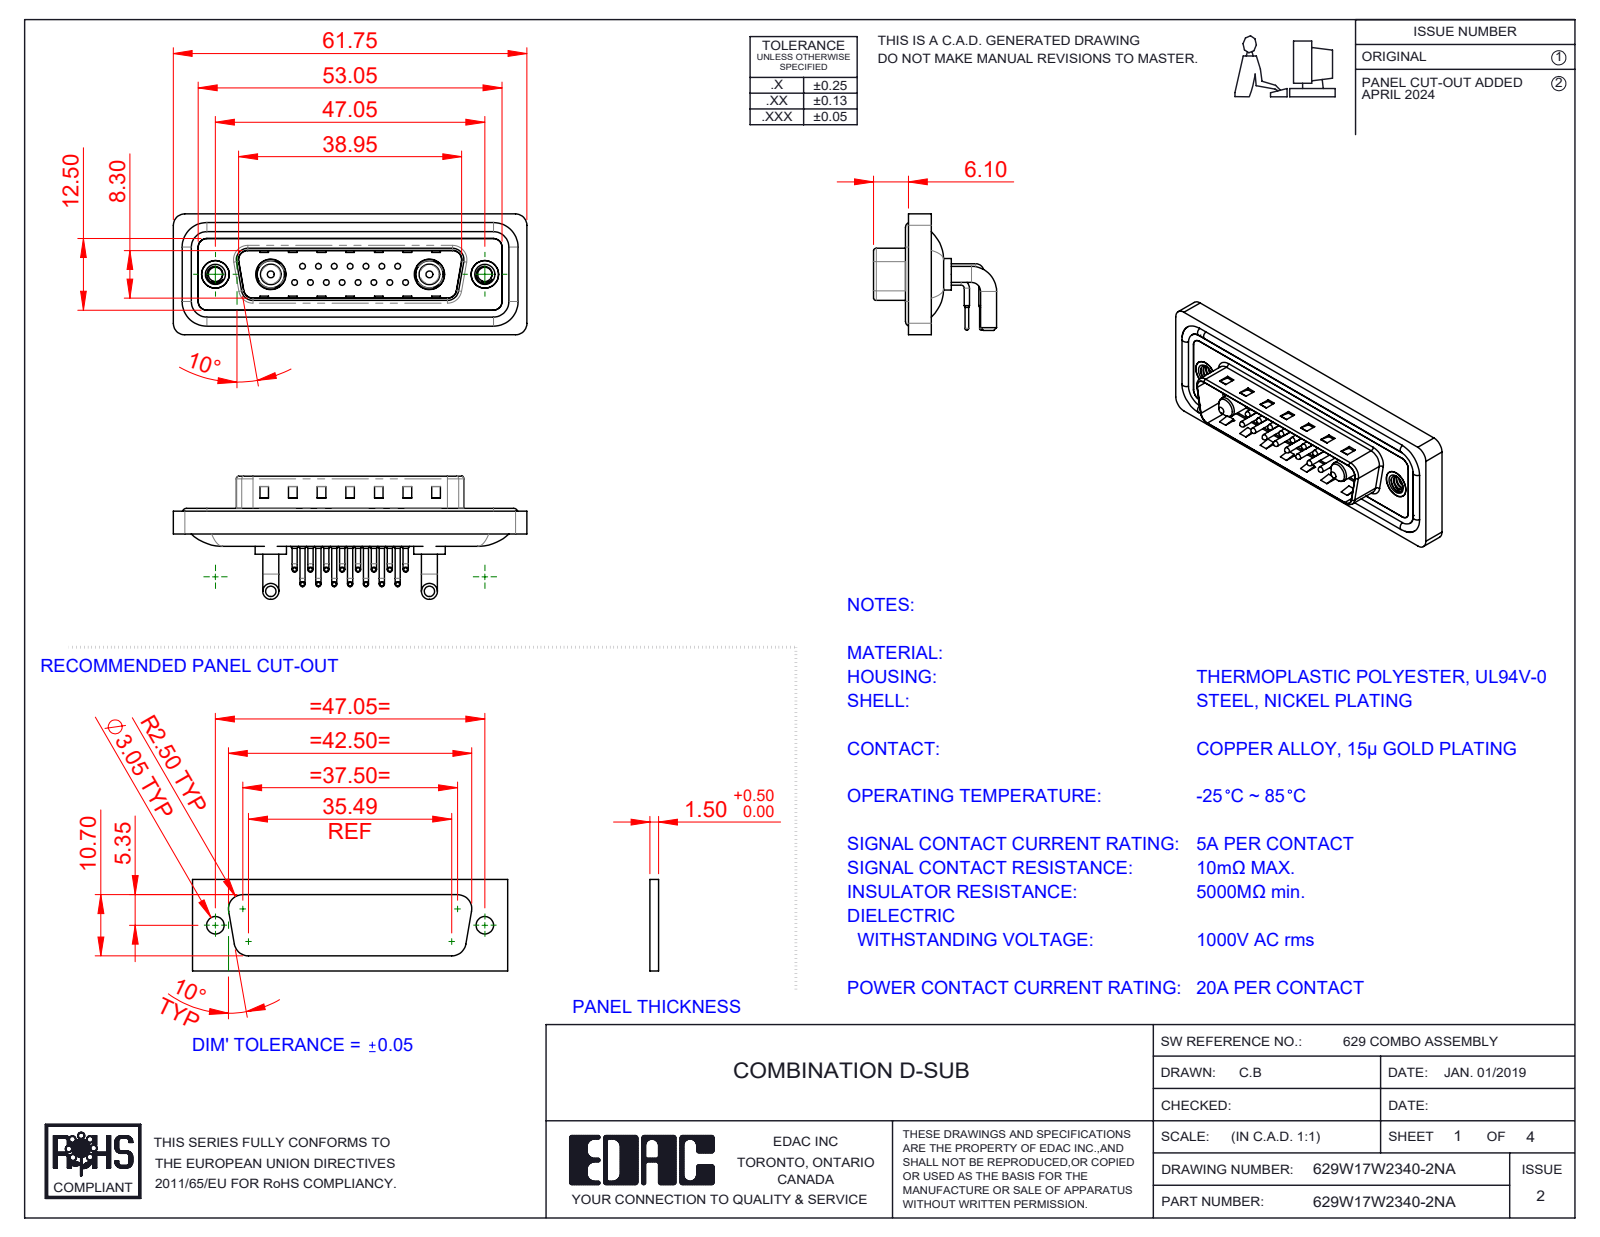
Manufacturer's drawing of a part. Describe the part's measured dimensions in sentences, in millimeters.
The part is named "629Combo Shell Front_25 Contacts; 629Combo Waterproof Housing_25 Contacts; 629Combo Shell Rear_25 Contacts; 629Combo Contact Row 1 (+5 more)". Its 3-D file was written by "SolidWorks 2023 (CONFIG_CONTROL_DESIGN)". It is 26 solids with 2213 faces: 1189 planar, 768 cylindrical and 256 other. Overall it measures 61.75 by 21.5 by 21.1 millimeters. Its volume is 7 516 cubic millimeters and its surface area 12 605 square millimeters. Round holes: 15 of diameter 0.75, 15 of diameter 1.6, 15 of diameter 2, 2 of diameter 2.5, 2 of diameter 4, 2 of diameter 4.8, 2 of diameter 4.85, 2 of diameter 5, 2 of diameter 5.3. Round bosses or shafts: 30 of diameter 0.9, 15 of diameter 1.5, 15 of diameter 1, 15 of diameter 0.65, 4 of diameter 2.8, 4 of diameter 1.6, 2 of diameter 5.5, 2 of diameter 5.2. Partial cylindrical surfaces (rounded edges, fillets, slot ends): 18 of radius 1.5, 18 of radius 2, 15 of radius 1.01, 8 of radius 0.5, 8 of radius 1.6, 4 of radius 0.25, 4 of radius 0.6, 4 of radius 0.65. The main face-to-face distances are 0.4, 2.9, 0.8, 4.1, 1.1, 2.1, 1.6, 4.5, 1.5, 2.5. The hole center spacings are 3.16, 2.77, 5.54, 8.31, 5.04, 7.49, 11.08, 5.03.
